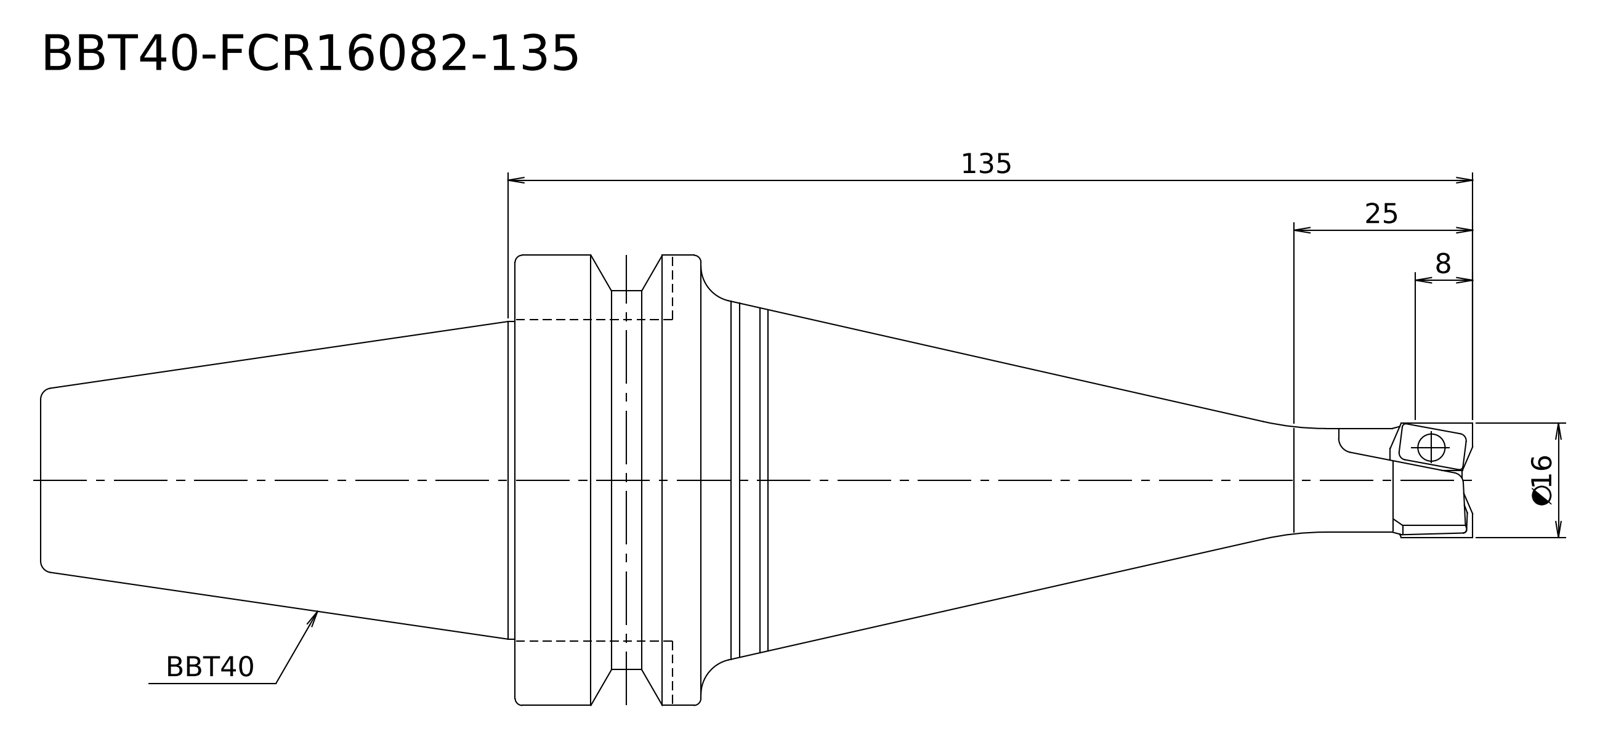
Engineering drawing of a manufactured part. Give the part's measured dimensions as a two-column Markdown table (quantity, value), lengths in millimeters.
| quantity | value |
| --- | --- |
| STEP written by | Kubotek KeyCreator V8.5.1 (14335) (CONFIG_CONTROL_DESIGN) |
| units | millimeters |
| bodies | 1 solid, 17 faces (4 planar, 6 cylindrical, 7 other) |
| overall size | 200.4 × 63 × 63 |
| volume | 225 837 mm³ |
| surface area | 26 453 mm² |
| round bosses / shafts (diameter × count) | 63 × 1, 53 × 1, 44.45 × 1, 16 × 1, 14.5 × 1 |
| main face-to-face distances | 66.4, 26, 92.4, 108, 134, 200.4 |
